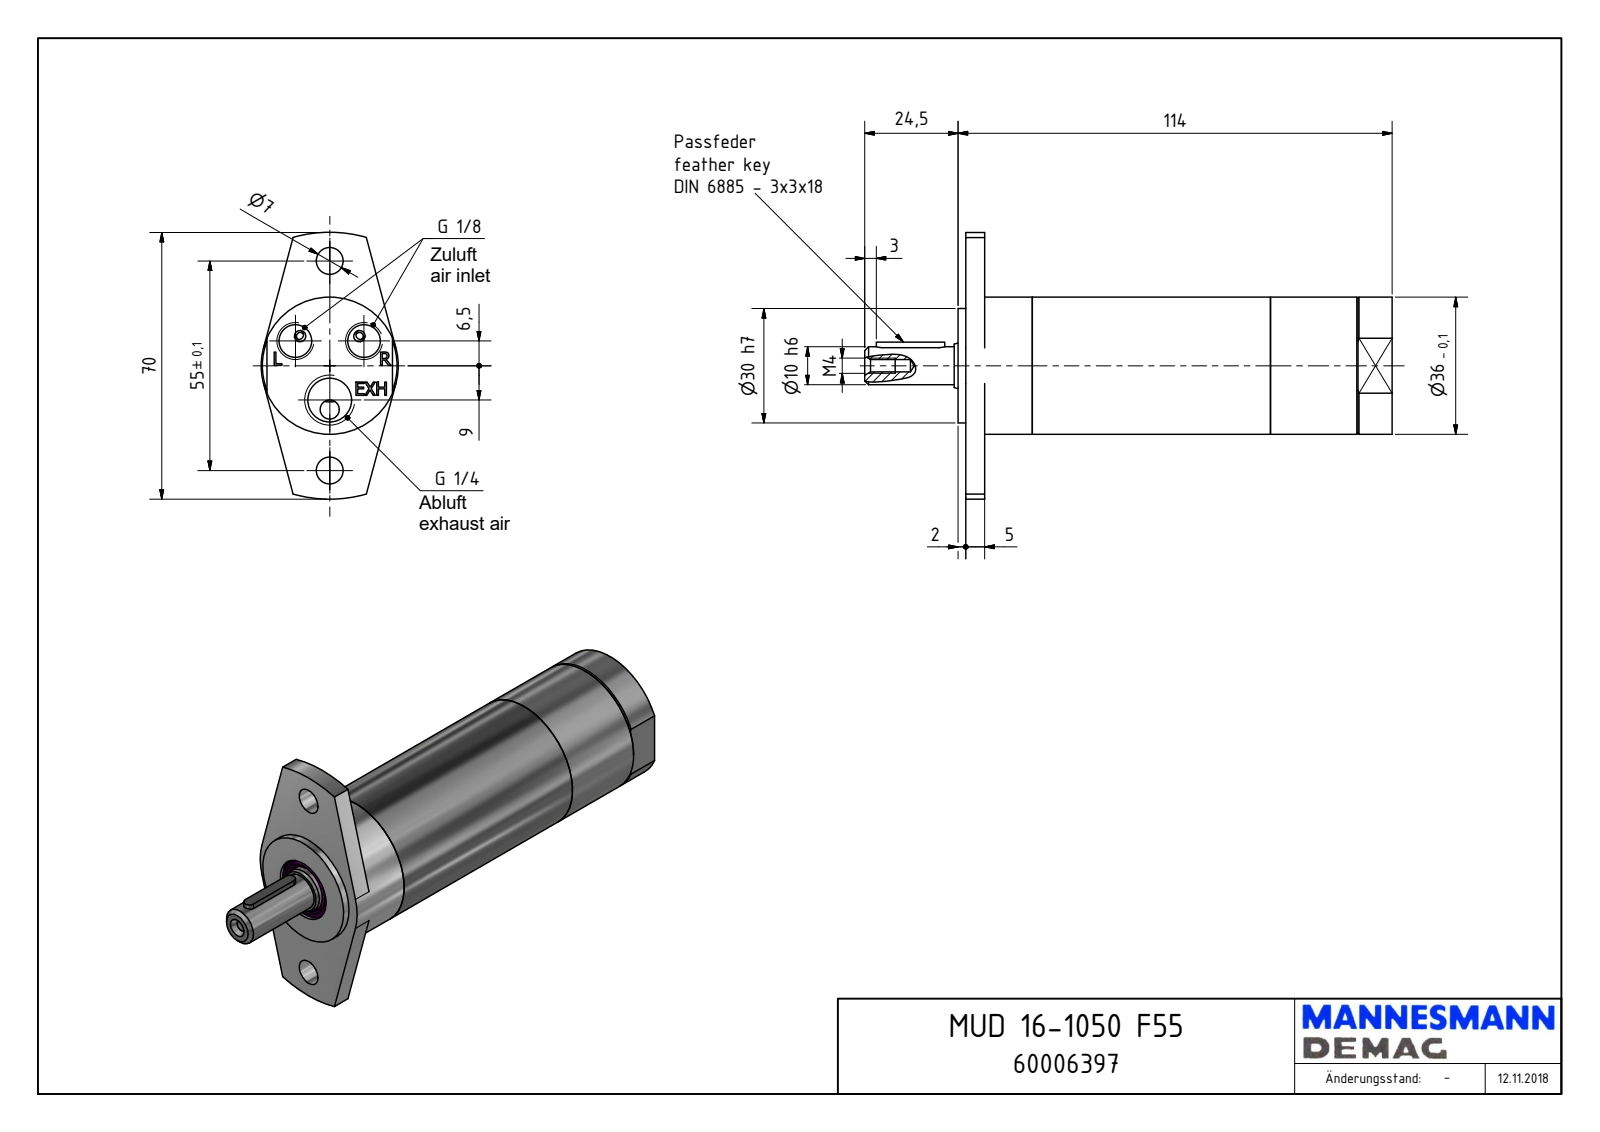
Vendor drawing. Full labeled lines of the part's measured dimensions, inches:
Part name (STEP PRODUCT): MUD 16-1050 F55_60006397
STEP written by: Autodesk Inventor 2018 (AUTOMOTIVE_DESIGN)
Units: inches
Bodies: 1 solid, 127 faces (84 planar, 22 cylindrical, 21 other)
Overall size (bounding box): 5.453 × 2.756 × 1.417
Volume: 7.247 in³ · Surface area: 30.08 in²
Round holes (diameter × count): ⌀0.276 ×2, ⌀0.337 ×2, ⌀0.128 ×1, ⌀0.451 ×1, ⌀0.61 ×1, ⌀0.669 ×1
Round bosses / shafts (diameter × count): ⌀1.417 ×1, ⌀1.181 ×1, ⌀0.47 ×1, ⌀0.394 ×1
Partial cylindrical surfaces — rounded edges, fillets, slot ends (radius × count): R0.059 ×2, R0.374 ×2, R1.378 ×1
Main face-to-face distances: 0.197, 4.409, 4.213, 0.079, 0.276, 4.488, 4.089, 4.011, 3.814, 0.399
Hole centre spacings: 0.437, 0.706, 0.9, 1.083, 1.385, 0.028, 0.353, 0.354
